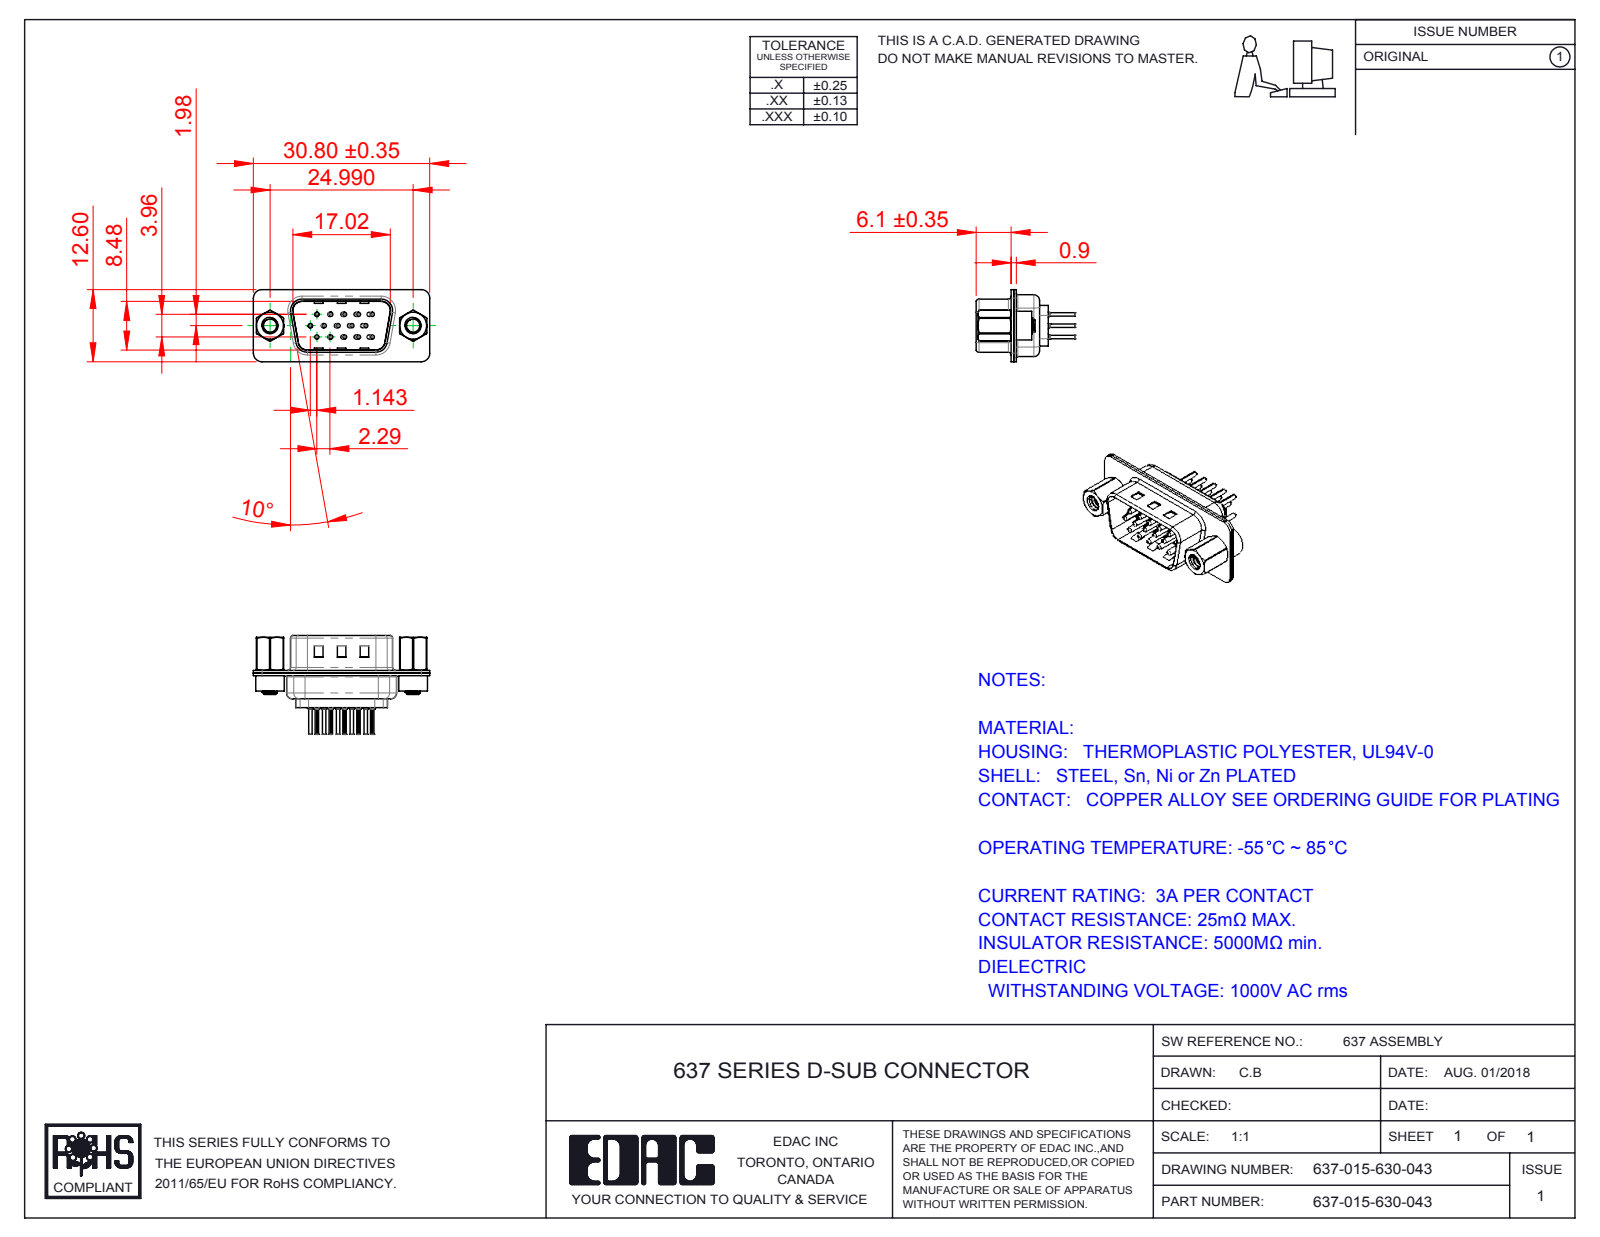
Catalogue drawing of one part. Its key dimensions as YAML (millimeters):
part_name: "637 Shell Front_15 Contacts; 637 Contact Row 1_30; 637 Contact Row 3_30; 637 Housing_15 Contacts (+5 more)"
step_written_by: "SolidWorks 2016 (CONFIG_CONTROL_DESIGN)"
units: millimeters
bodies: {solids: 22, faces: 1930, planar: 489, cylindrical: 756, other: 685}
overall_size: [30.8, 17.25, 12.6]
volume: 1529
surface_area: 5130
round_holes:
  - {diameter: 1.6, count: 27}
  - {diameter: 0.2, count: 15}
  - {diameter: 0.35, count: 15}
  - {diameter: 1.1, count: 15}
  - {diameter: 0.75, count: 12}
  - {diameter: 2, count: 12}
  - {diameter: 2.26, count: 2}
  - {diameter: 2.29, count: 2}
  - {diameter: 4, count: 2}
  - {diameter: 4.8, count: 2}
round_bosses_or_shafts:
  - {diameter: 2, count: 15}
  - {diameter: 1.5, count: 15}
  - {diameter: 0.75, count: 15}
  - {diameter: 0.6, count: 15}
  - {diameter: 5, count: 2}
  - {diameter: 4.9, count: 2}
  - {diameter: 2.79, count: 2}
partial_cylinders:
  - {radius: 0.1, count: 30}
  - {radius: 1.5, count: 16}
  - {radius: 2, count: 12}
  - {radius: 0.5, count: 8}
  - {radius: 0.25, count: 4}
  - {radius: 0.55, count: 4}
  - {radius: 0.7, count: 4}
  - {radius: 0.95, count: 4}
face_to_face_distances: [0.45, 0.9, 0.4, 8.48, 0.7, 8.88, 0.31, 4.55, 1.05, 6.5]
hole_center_spacings: [3.96, 2.29, 2.28, 4.57, 2.42, 6.05, 4.84, 2.35]
